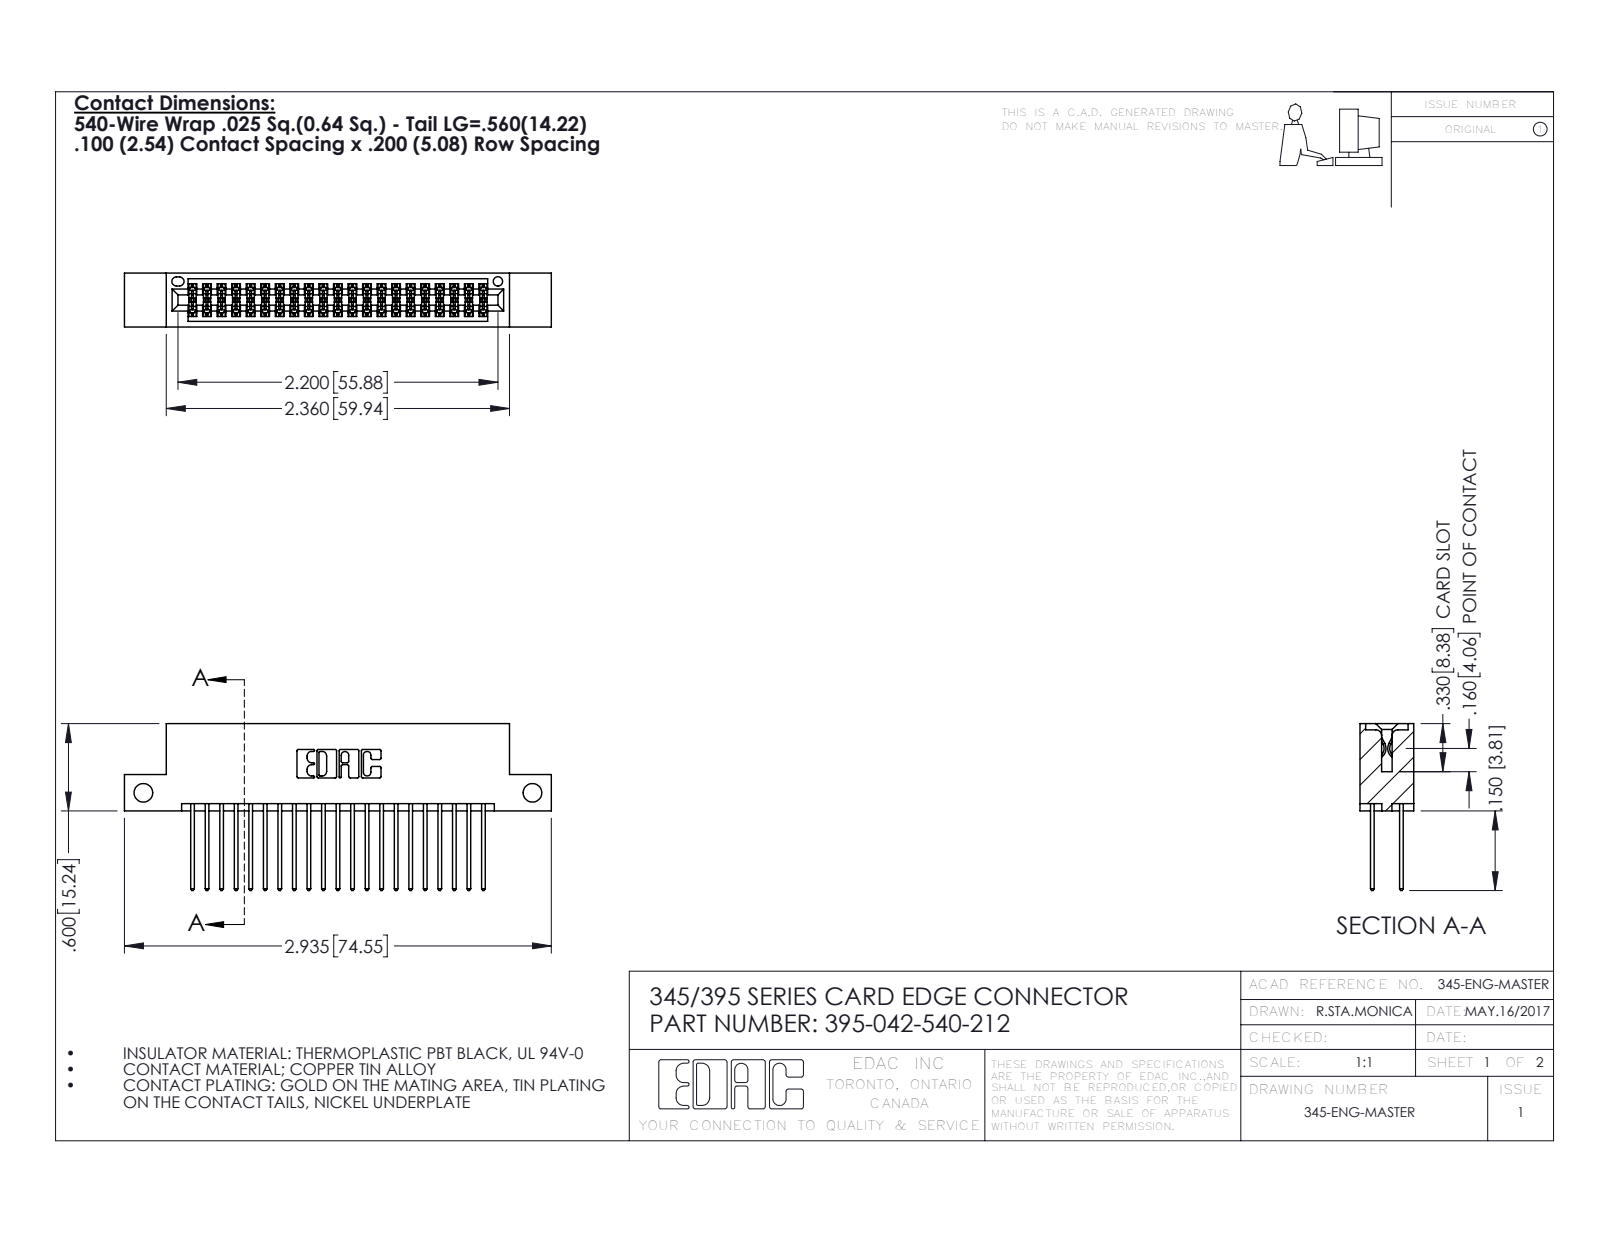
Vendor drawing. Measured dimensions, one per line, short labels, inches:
name: 345 Part_Flush Mounting Lugs - Side Mount; 345-292-001_345-293-140; 395-042-540-212
written by: SolidWorks 2016 (CONFIG_CONTROL_DESIGN)
unit: in
bodies: 43 solids, 2226 faces (1466 planar, 760 cylindrical, 0 other)
size: 2.935 × 1.147 × 0.37
volume: 0.434 in³; area: 16.61 in²
holes: 2× ⌀0.128, 1× ⌀0.064
rounds: 63× R0.006, 42× R0.01, 22× R0.01, 6× R0.007, 6× R0.031, 3× R0.026, 2× R0.014, 2× R0.019
face distances: 0.298, 0.072, 0.2, 0.098, 0.272, 0.025, 0.37, 0.225, 0.175, 0.149
hole spacings: 2.675
